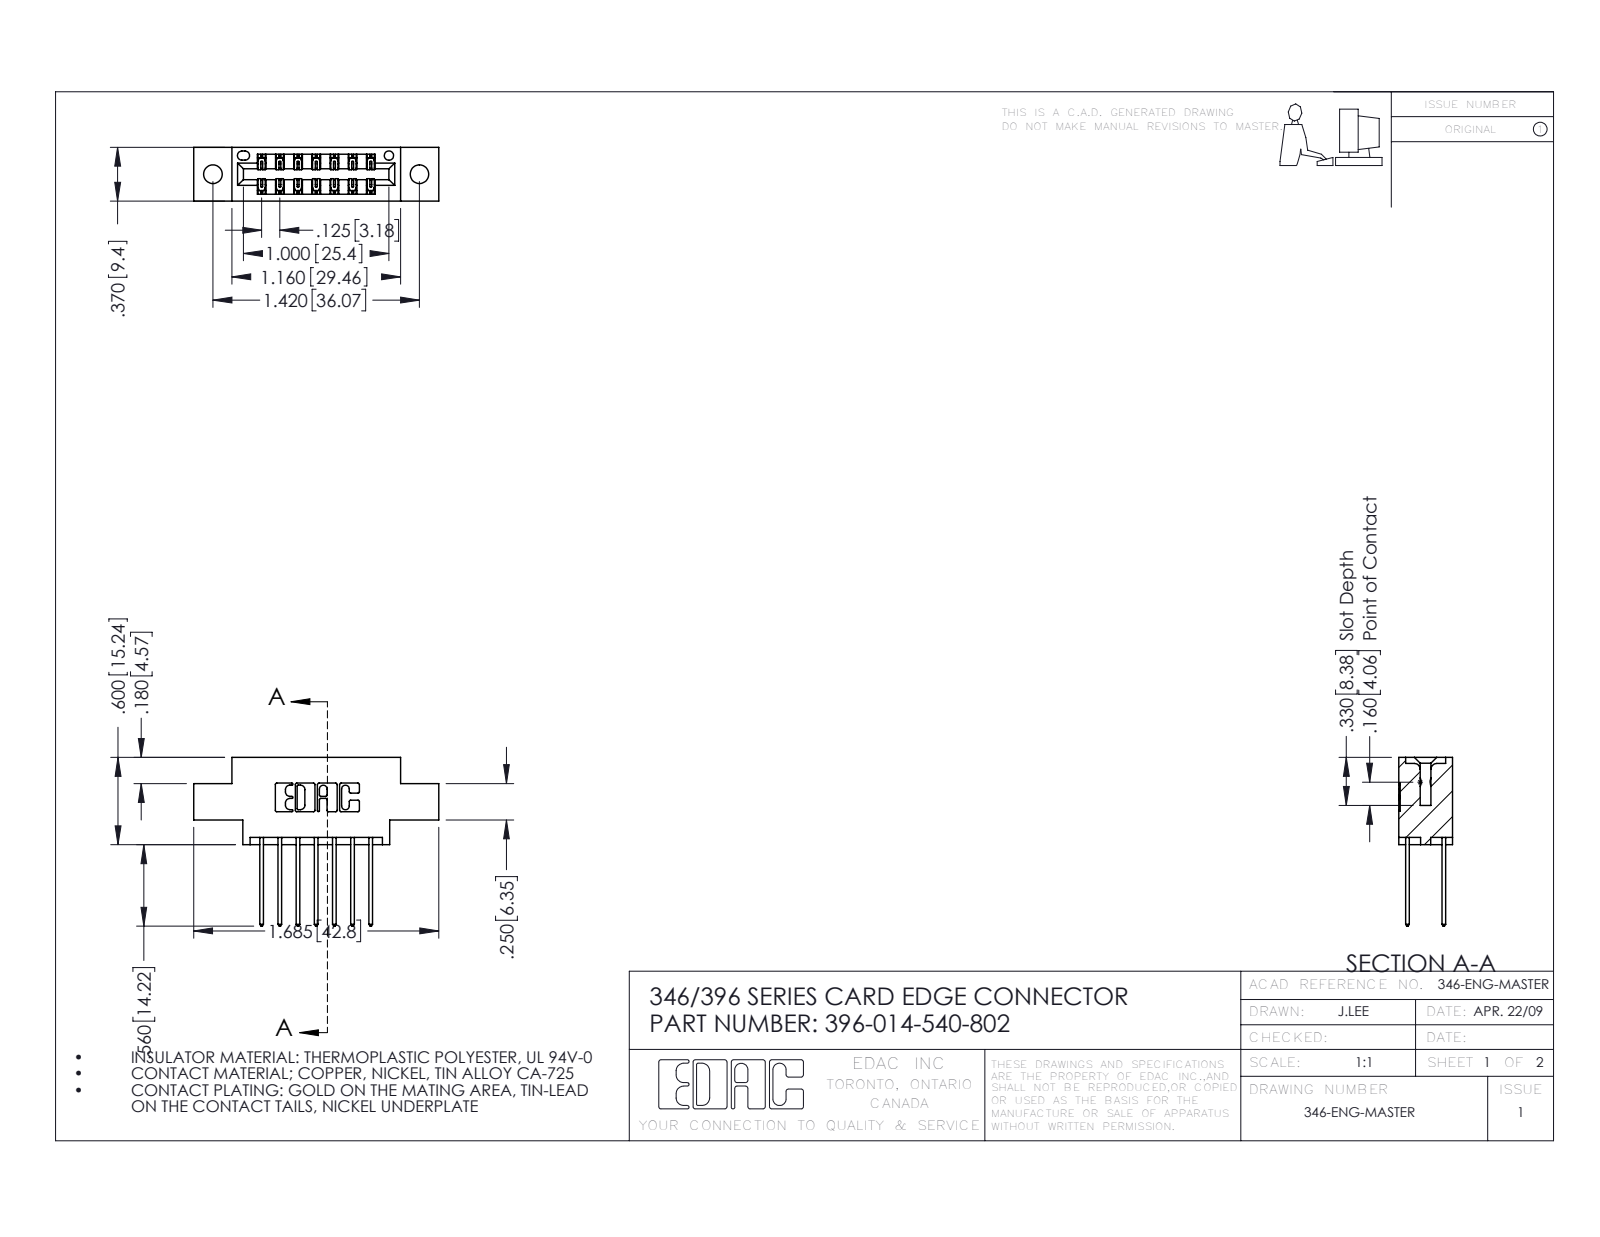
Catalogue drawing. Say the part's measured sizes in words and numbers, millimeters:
The part is named "396-014-540-802; 346 Part_0.170 Offset - 0.128 Dia; 345-292-001_345-293-140". Its 3-D file was written by "SolidWorks 2016 (CONFIG_CONTROL_DESIGN)". It is 15 solids with 854 faces: 570 planar, 284 cylindrical and 0 other. Overall it measures 42.8 by 29.5 by 9.4 millimeters. Its volume is 3 770 cubic millimeters and its surface area 4 785 square millimeters. Round holes: 2 of diameter 3.3, 1 of diameter 1.6. Partial cylindrical surfaces (rounded edges, fillets, slot ends): 22 of radius 0.3, 21 of radius 0.2, 14 of radius 0.3, 6 of radius 0.2, 6 of radius 0.8, 3 of radius 0.7, 2 of radius 0.4, 2 of radius 0.6. The main face-to-face distances are 6.4, 1.2, 8.2, 9.4, 1.8, 7.6, 0.6, 7, 5.7, 3.8. The hole center spacings are 6.2, 30.9, 36.1.
